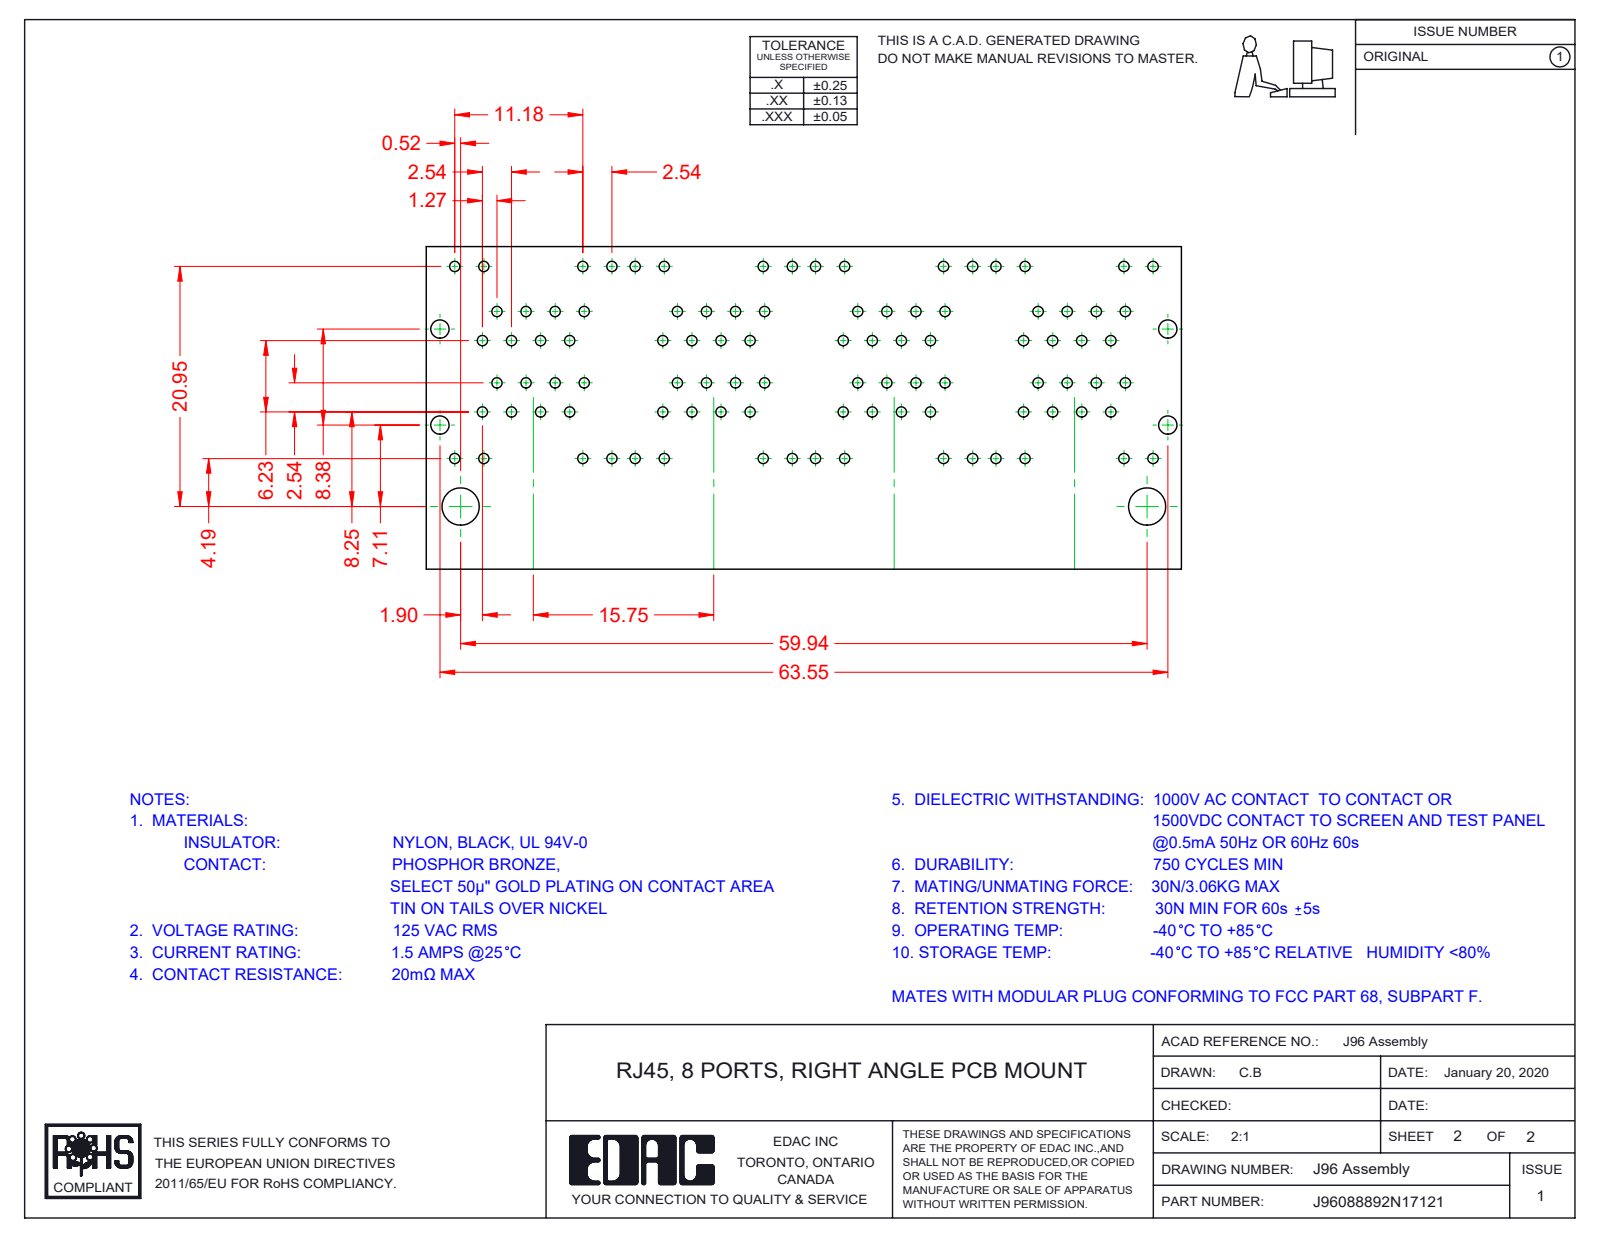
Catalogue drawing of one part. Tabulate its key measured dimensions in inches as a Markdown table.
| quantity | value |
| --- | --- |
| part name | 96 Contact Lock Upper; 96 Contacts Upper; 96 LED RH Lower_7-Green-Orange; 96 LED RH Upper_7-Green-Orange (+8 more) |
| STEP written by | SolidWorks 2016 (CONFIG_CONTROL_DESIGN) |
| units | inches |
| bodies | 96 solids, 7658 faces (6069 planar, 1323 cylindrical, 266 other) |
| overall size | 2.522 × 1.165 × 1.129 |
| volume | 1.474 in³ |
| surface area | 98.67 in² |
| round holes (diameter × count) | 0.067 × 3 |
| round bosses / shafts (diameter × count) | 0.066 × 3 |
| partial cylindrical surfaces (radius × count) | 0.01 × 124, 0.014 × 73, 0.039 × 72, 0.02 × 49, 0.036 × 32, 0.008 × 21, 0.028 × 11, 0.009 × 8 |
| main face-to-face distances | 0.62, 0.014, 0.392, 0.046, 0.063, 0.021, 0.393, 0.401, 0.499, 0.133 |
| hole center spacings | 0.62, 1.24 |
